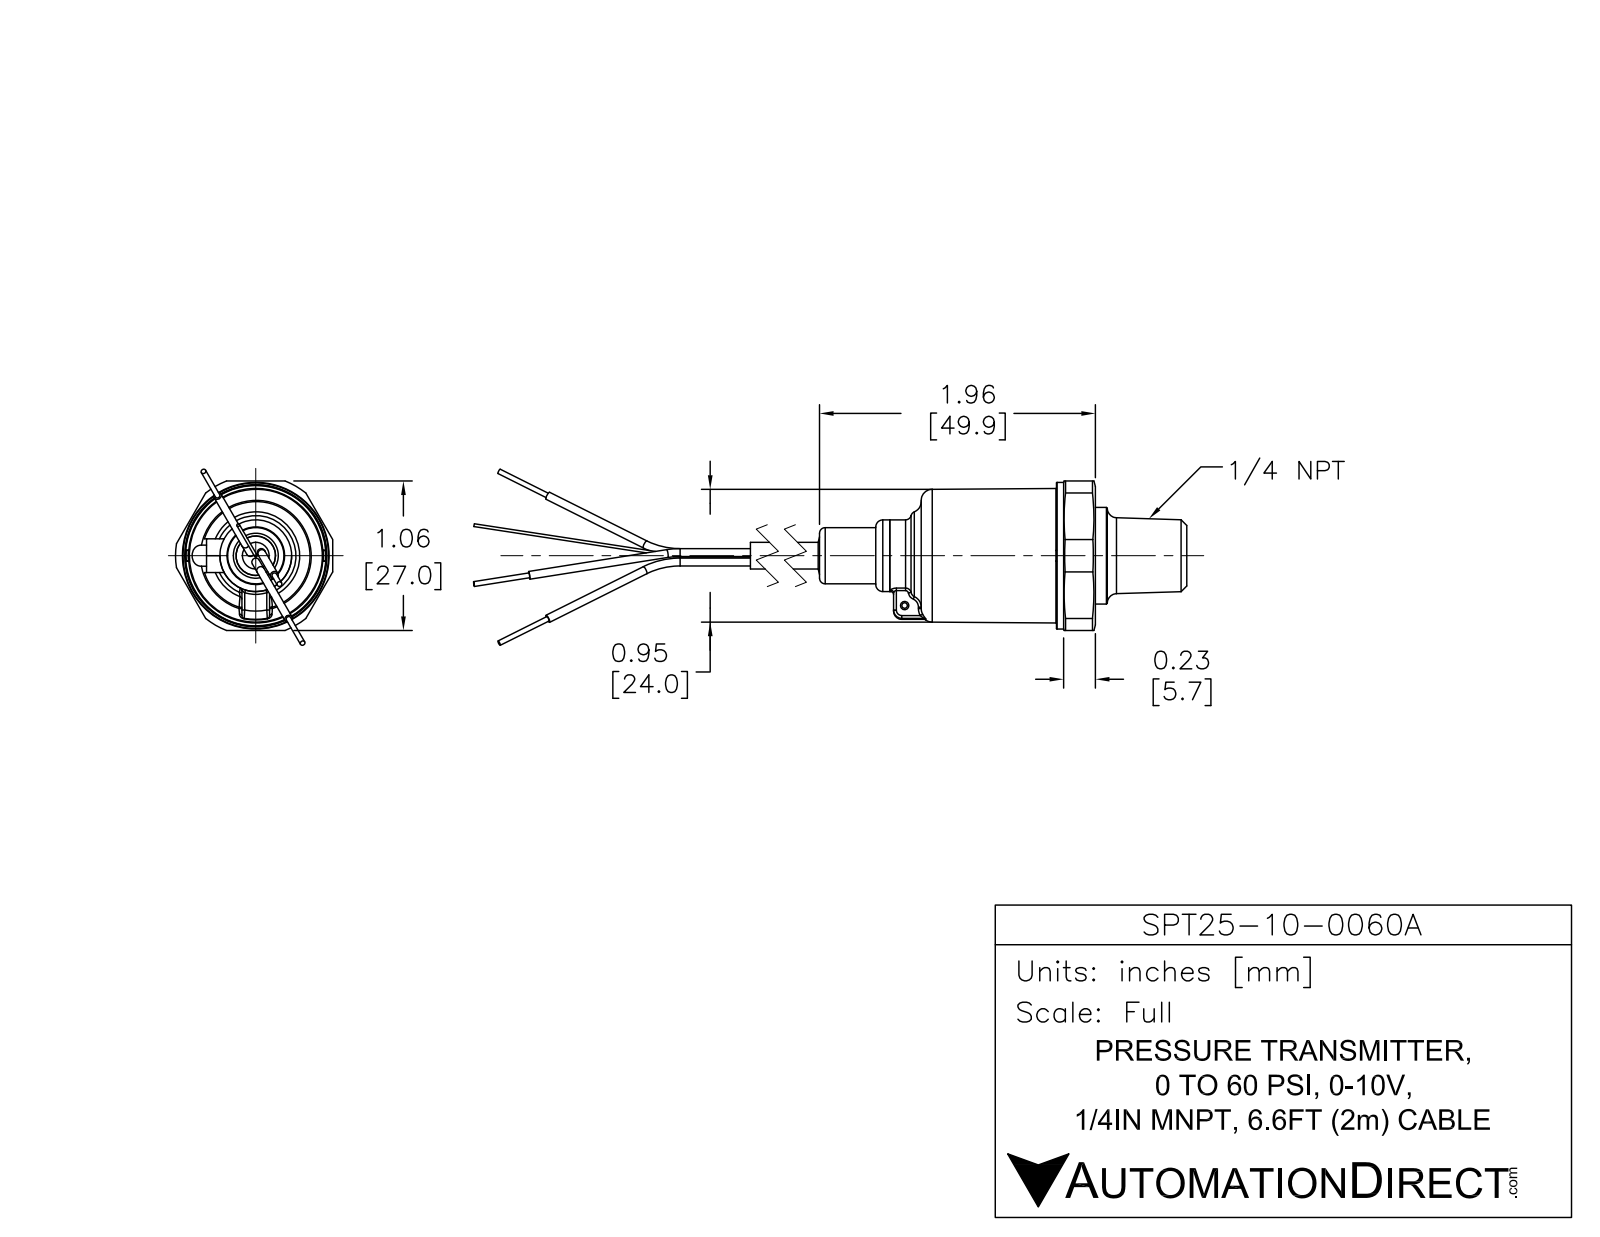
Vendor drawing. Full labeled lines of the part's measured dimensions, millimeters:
Part name (STEP PRODUCT): SPT25-10-0060A
STEP written by: SolidWorks 2017 (AUTOMOTIVE_DESIGN)
Units: millimetres
Bodies: 7 solids, 116 faces (32 planar, 49 cylindrical, 35 other)
Overall size (bounding box): 153.3 × 29 × 27.09
Volume: 20 801 mm³ · Surface area: 7 170 mm²
Round holes (diameter × count): ⌀1 ×1, ⌀3.3 ×1
Round bosses / shafts (diameter × count): ⌀1.4 ×6, ⌀0.75 ×5, ⌀26.75 ×1, ⌀24 ×1, ⌀17.5 ×1, ⌀14 ×1, ⌀13 ×1, ⌀10 ×1
Partial cylindrical surfaces — rounded edges, fillets, slot ends (radius × count): R2 ×1, R14.5 ×1
Main face-to-face distances: 6.75, 24, 17.25, 42.75, 49.5, 66.75, 44, 1.25, 5.5, 22.75
